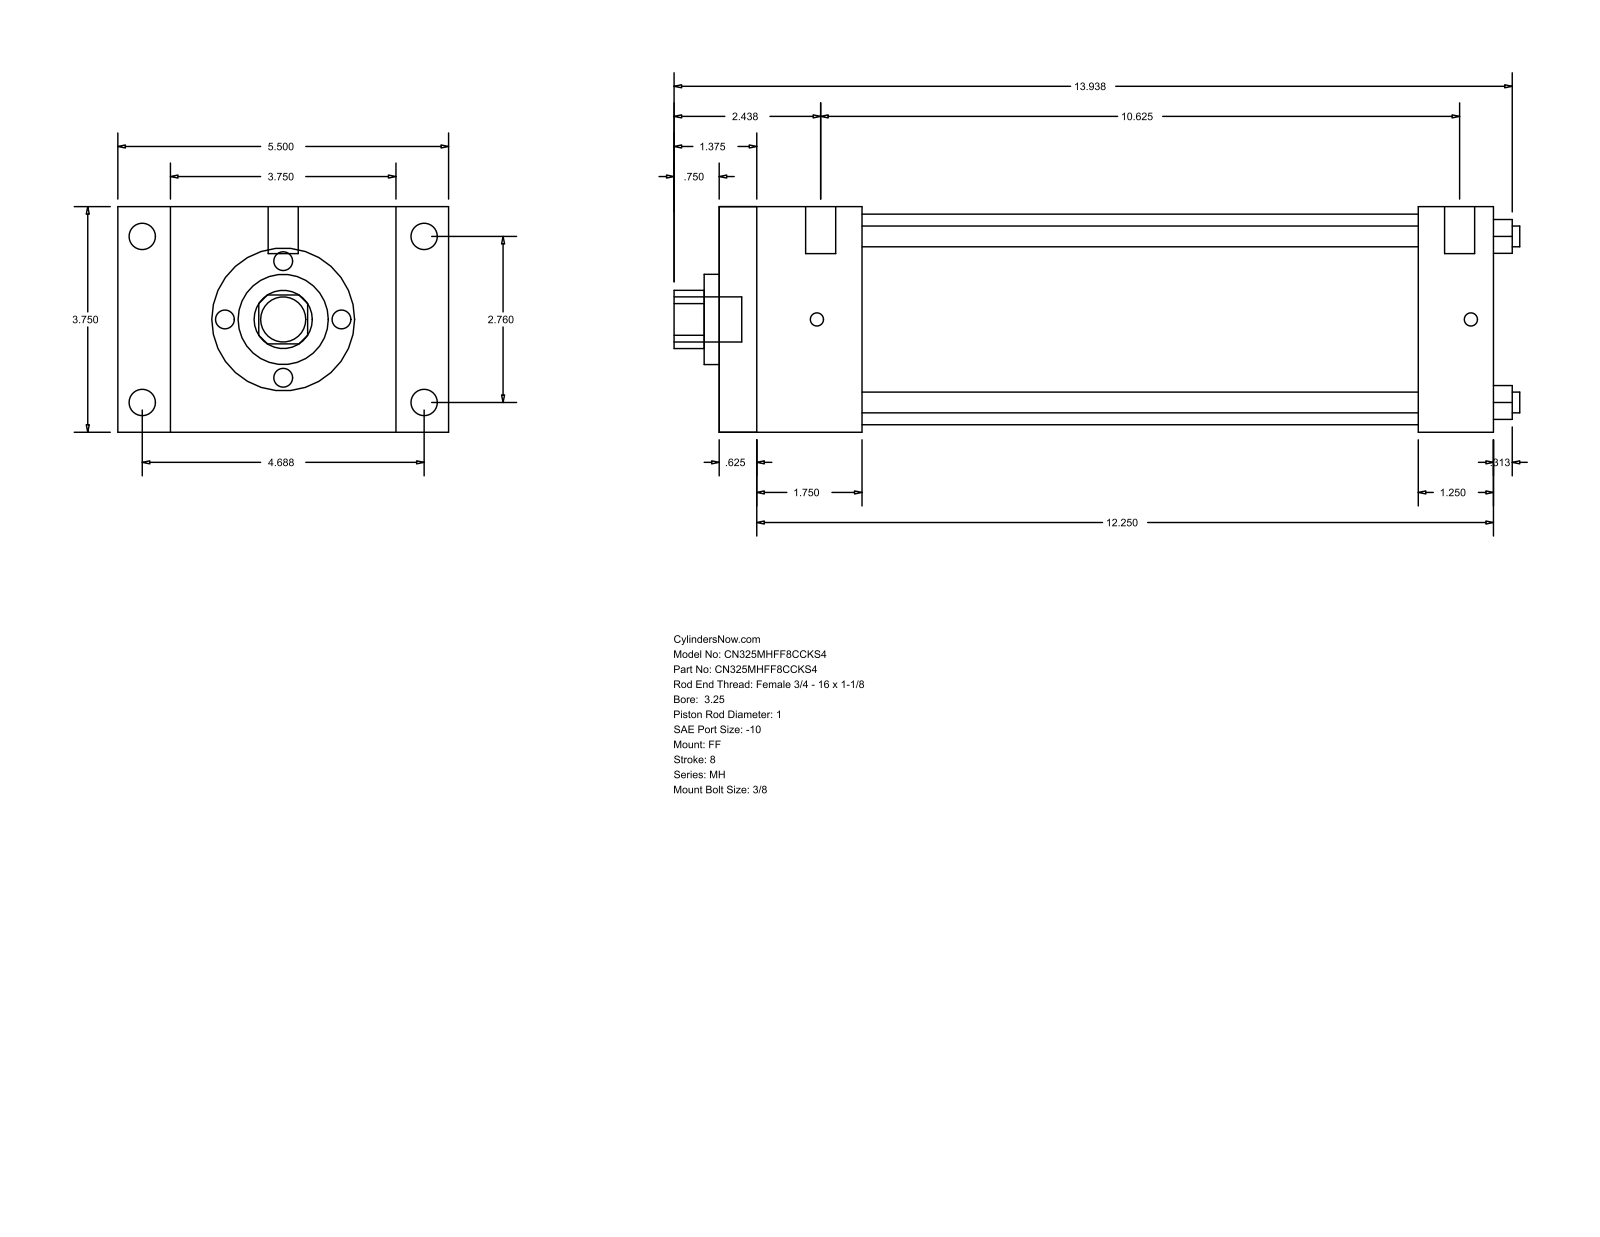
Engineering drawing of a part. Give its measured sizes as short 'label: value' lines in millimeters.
name: MH_FF__0325_1
written by: GSSL Pune (CONFIG_CONTROL_DESIGN)
unit: mm
bodies: 0 solids, 92 faces (64 planar, 28 cylindrical, 0 other)
size: 357.19 × 139.7 × 95.25
holes: 4× ⌀8.76, 1× ⌀25.4, 1× ⌀38.1, 1× ⌀88.9
bosses: 4× ⌀11.13, 4× ⌀5.56, 2× ⌀12.7, 1× ⌀19.05
rounds: 1× R12.29
face distances: 95.24, 327.02, 15.87, 311.15, 22.23, 117.47, 295.27, 279.4, 31.75, 60.33
hole spacings: 49.57, 70.1, 99.14
